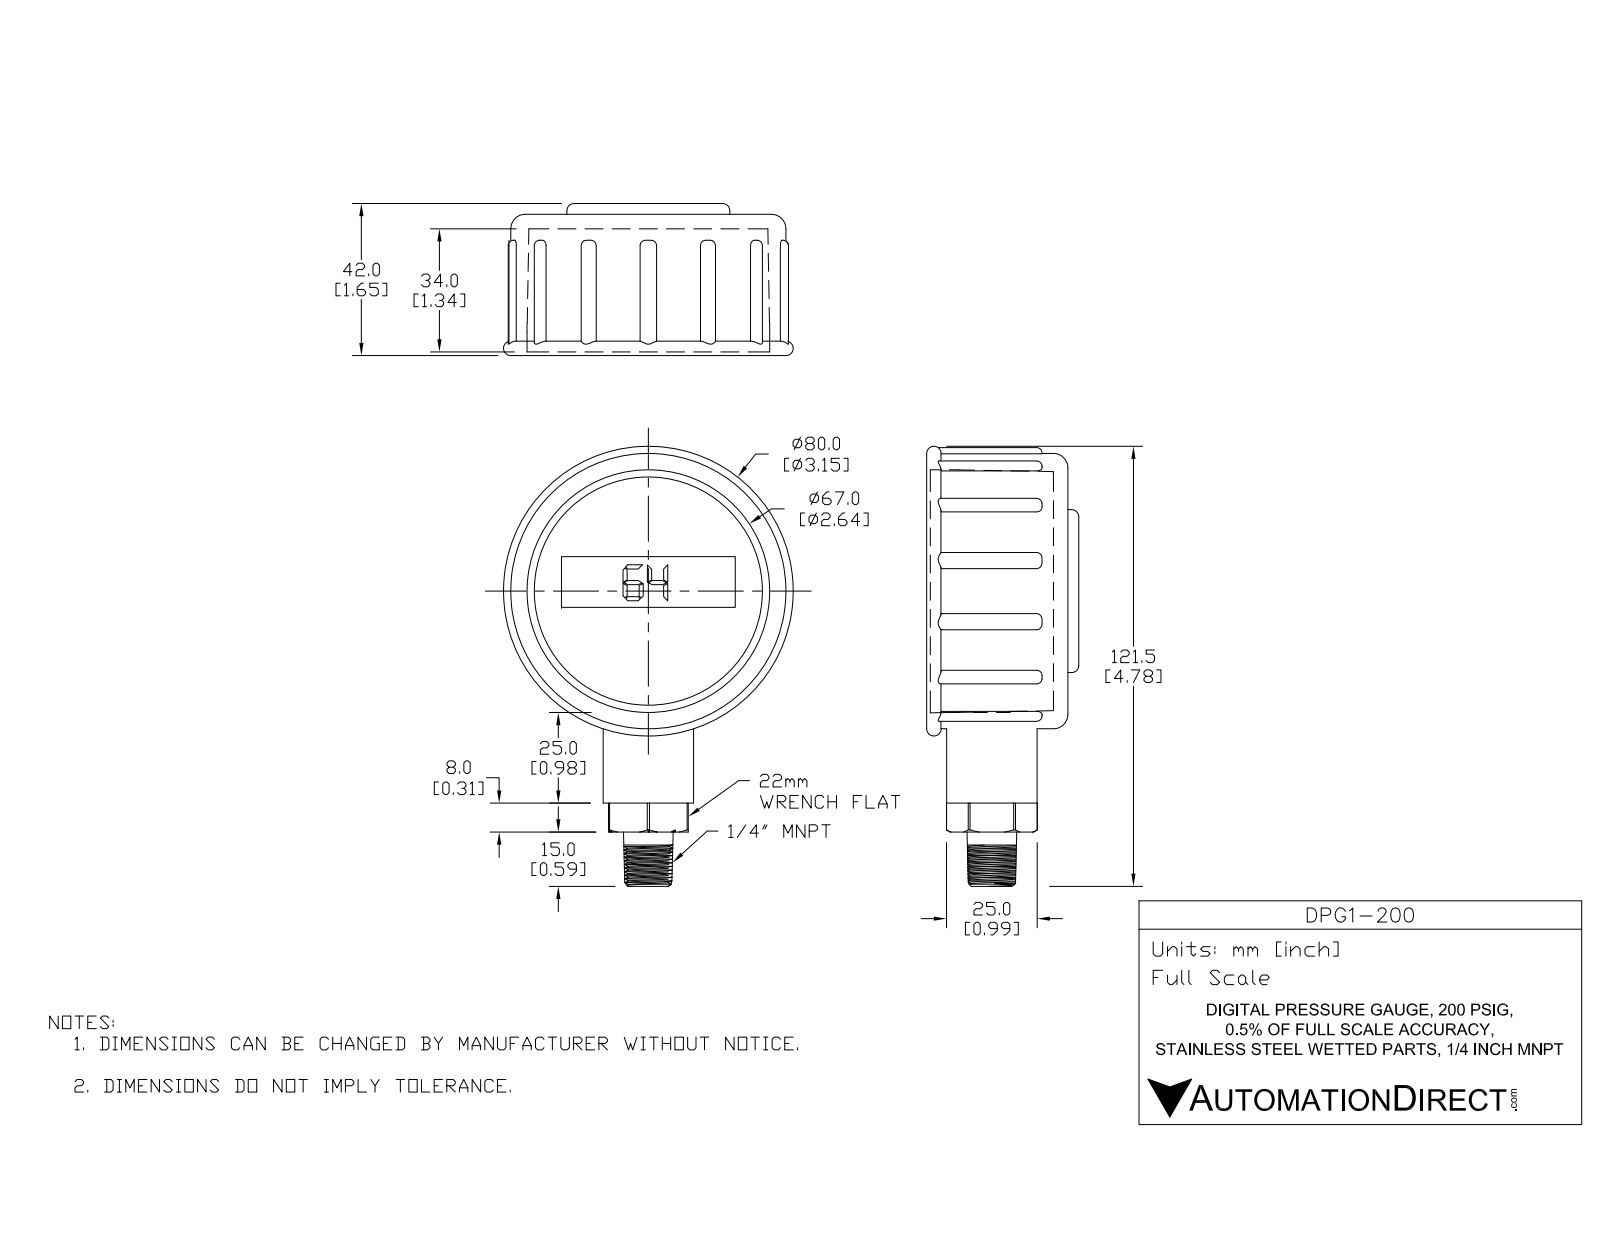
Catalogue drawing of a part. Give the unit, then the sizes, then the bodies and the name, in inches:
Units: inches
Overall size (bounding box): 4.788 × 3.15 × 1.654
Round holes (diameter × count): ⌀2.48 ×1, ⌀2.645 ×1
Round bosses / shafts (diameter × count): ⌀2.992 ×1, ⌀2.638 ×1, ⌀1.772 ×1, ⌀0.984 ×1, ⌀0.394 ×1
Partial cylindrical surfaces — rounded edges, fillets, slot ends (radius × count): R0.094 ×13, R0.335 ×6, R1.496 ×1
Main face-to-face distances: 1.337, 0.157, 1.494, 0.118, 0.276, 1.612, 1.654, 1.535, 1.378, 0.041
Volume: 11.97 in³ · Surface area: 71.27 in²
Bodies: 4 solids, 181 faces (71 planar, 49 cylindrical, 61 other)
Part name (STEP PRODUCT): DPG1-200
STEP written by: SolidWorks 2021 (CONFIG_CONTROL_DESIGN)
